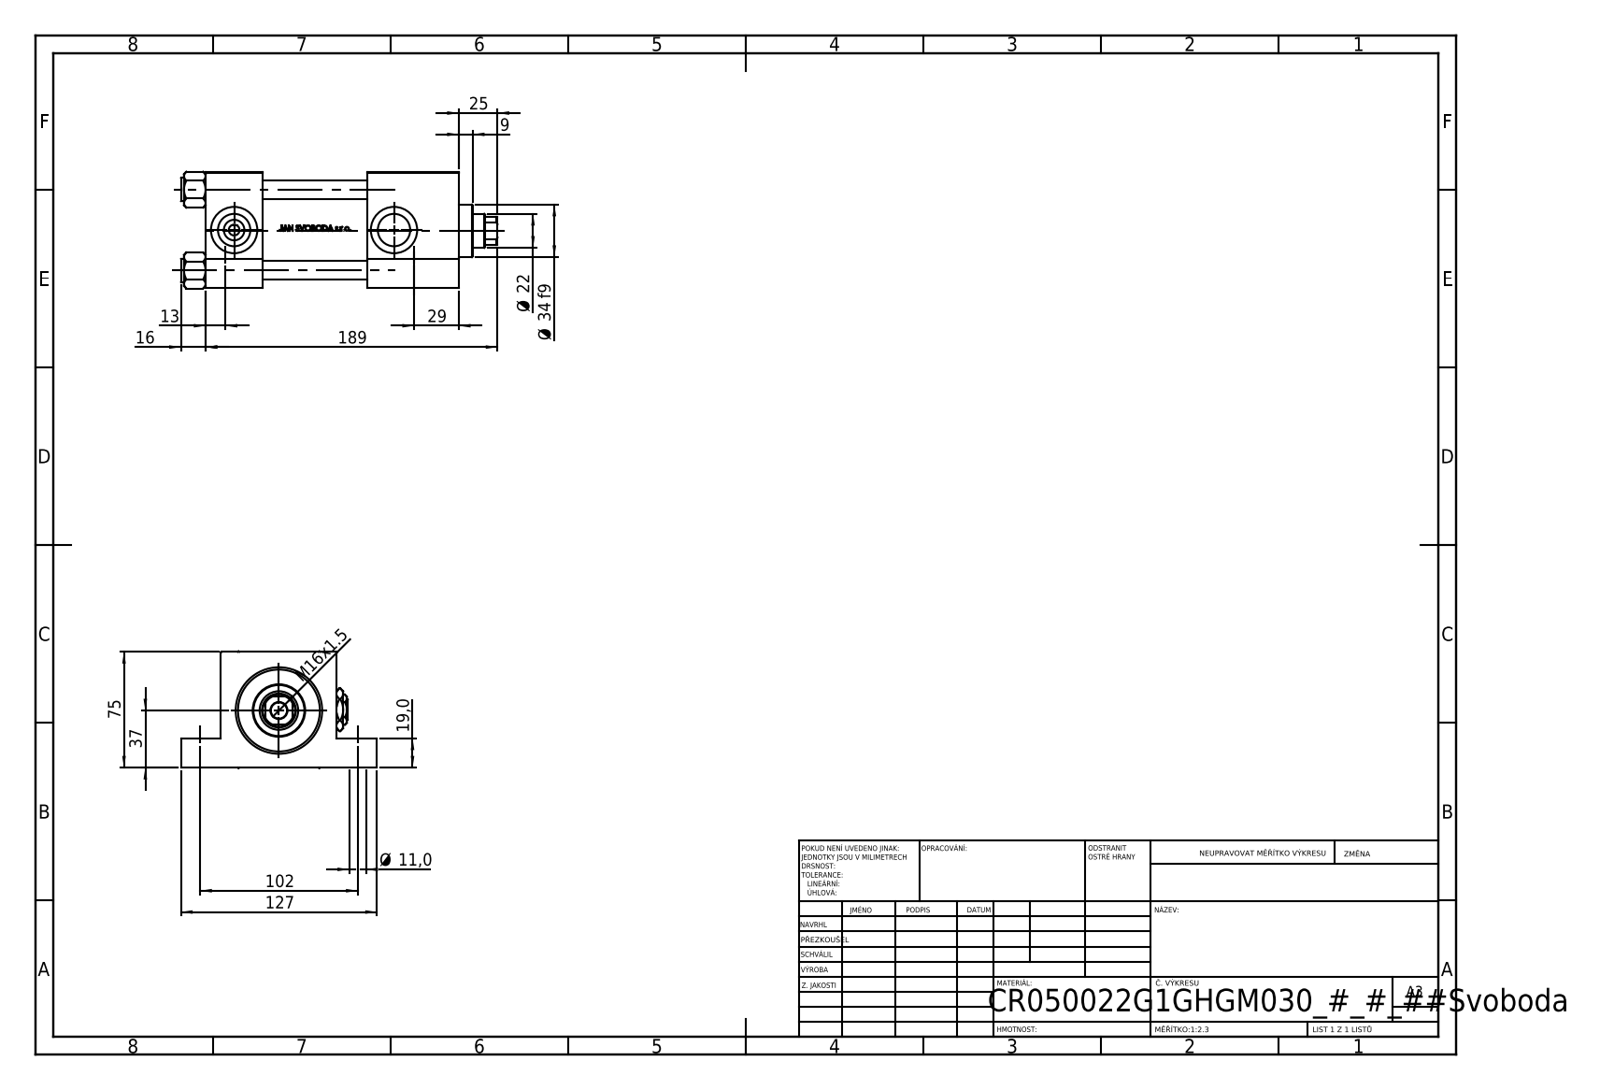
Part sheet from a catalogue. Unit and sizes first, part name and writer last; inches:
Units: inches
Overall size (bounding box): 8.071 × 5 × 2.974
Round holes (diameter × count): ⌀0.433 ×4, ⌀0.472 ×4, ⌀0.276 ×2, ⌀0.825 ×2, ⌀1.181 ×2, ⌀0.413 ×1, ⌀0.866 ×1, ⌀0.984 ×1, ⌀1.614 ×1, ⌀1.969 ×1, ⌀2.087 ×1
Round bosses / shafts (diameter × count): ⌀0.591 ×4, ⌀2.205 ×1, ⌀1.339 ×1
Partial cylindrical surfaces — rounded edges, fillets, slot ends (radius × count): R0.413 ×1
Main face-to-face distances: 2.953, 5, 1.457, 6.457, 0.748, 2.677, 2.205, 2.323, 4.134, 1.024
Hole centre spacings: 2.059, 1.442, 1.47, 2.912, 4.016, 4.803, 6.261, 4.075
Volume: 46.73 in³ · Surface area: 258.6 in²
Bodies: 12 solids, 1134 faces (454 planar, 128 cylindrical, 552 other)
Part name (STEP PRODUCT): V215CR_G_TYCINKA; NUT_M5_G; V215CR_G_Body; V215CR_VCP_G (+2 more)
STEP written by: SolidWorks 2019 (CONFIG_CONTROL_DESIGN)
